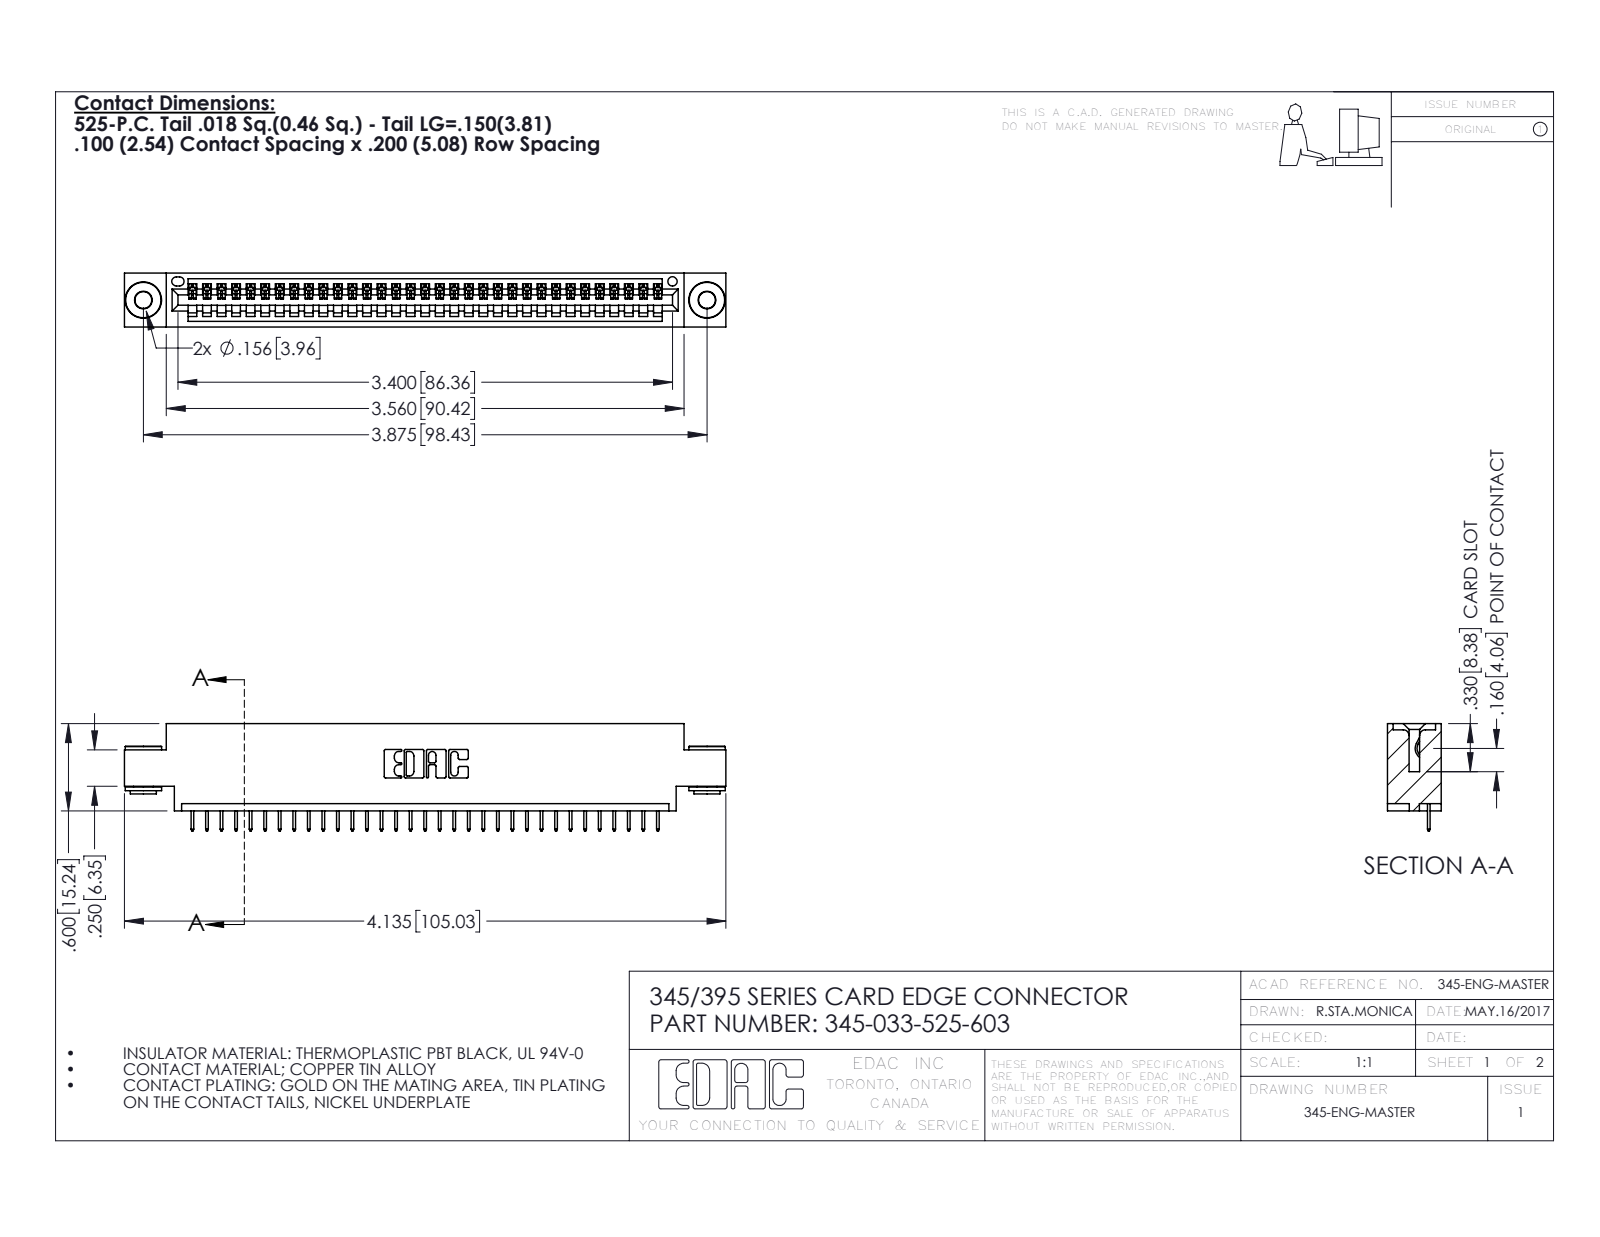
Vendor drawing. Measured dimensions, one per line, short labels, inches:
name: 345-250-002_345-250-002-102; 345-033-525-603; 345-292-001_345-293-125; 345 Part_0.170 Offset - 0.156 Dia-TH
written by: SolidWorks 2020 (CONFIG_CONTROL_DESIGN)
unit: in
bodies: 36 solids, 2214 faces (1612 planar, 594 cylindrical, 8 other)
size: 4.135 × 0.737 × 0.37
volume: 0.59 in³; area: 19.57 in²
holes: 2× ⌀0.116, 2× ⌀0.156, 1× ⌀0.064
bosses: 2× ⌀0.25, 2× ⌀0.18, 2× ⌀0.136
rounds: 66× R0.006, 22× R0.01, 6× R0.007, 6× R0.031, 3× R0.026, 2× R0.031, 2× R0.04, 1× R0.014
face distances: 0.072, 0.298, 0.37, 0.2, 0.098, 0.272, 0.025, 0.225, 0.175, 0.072
hole spacings: 0.27, 3.64, 3.875
